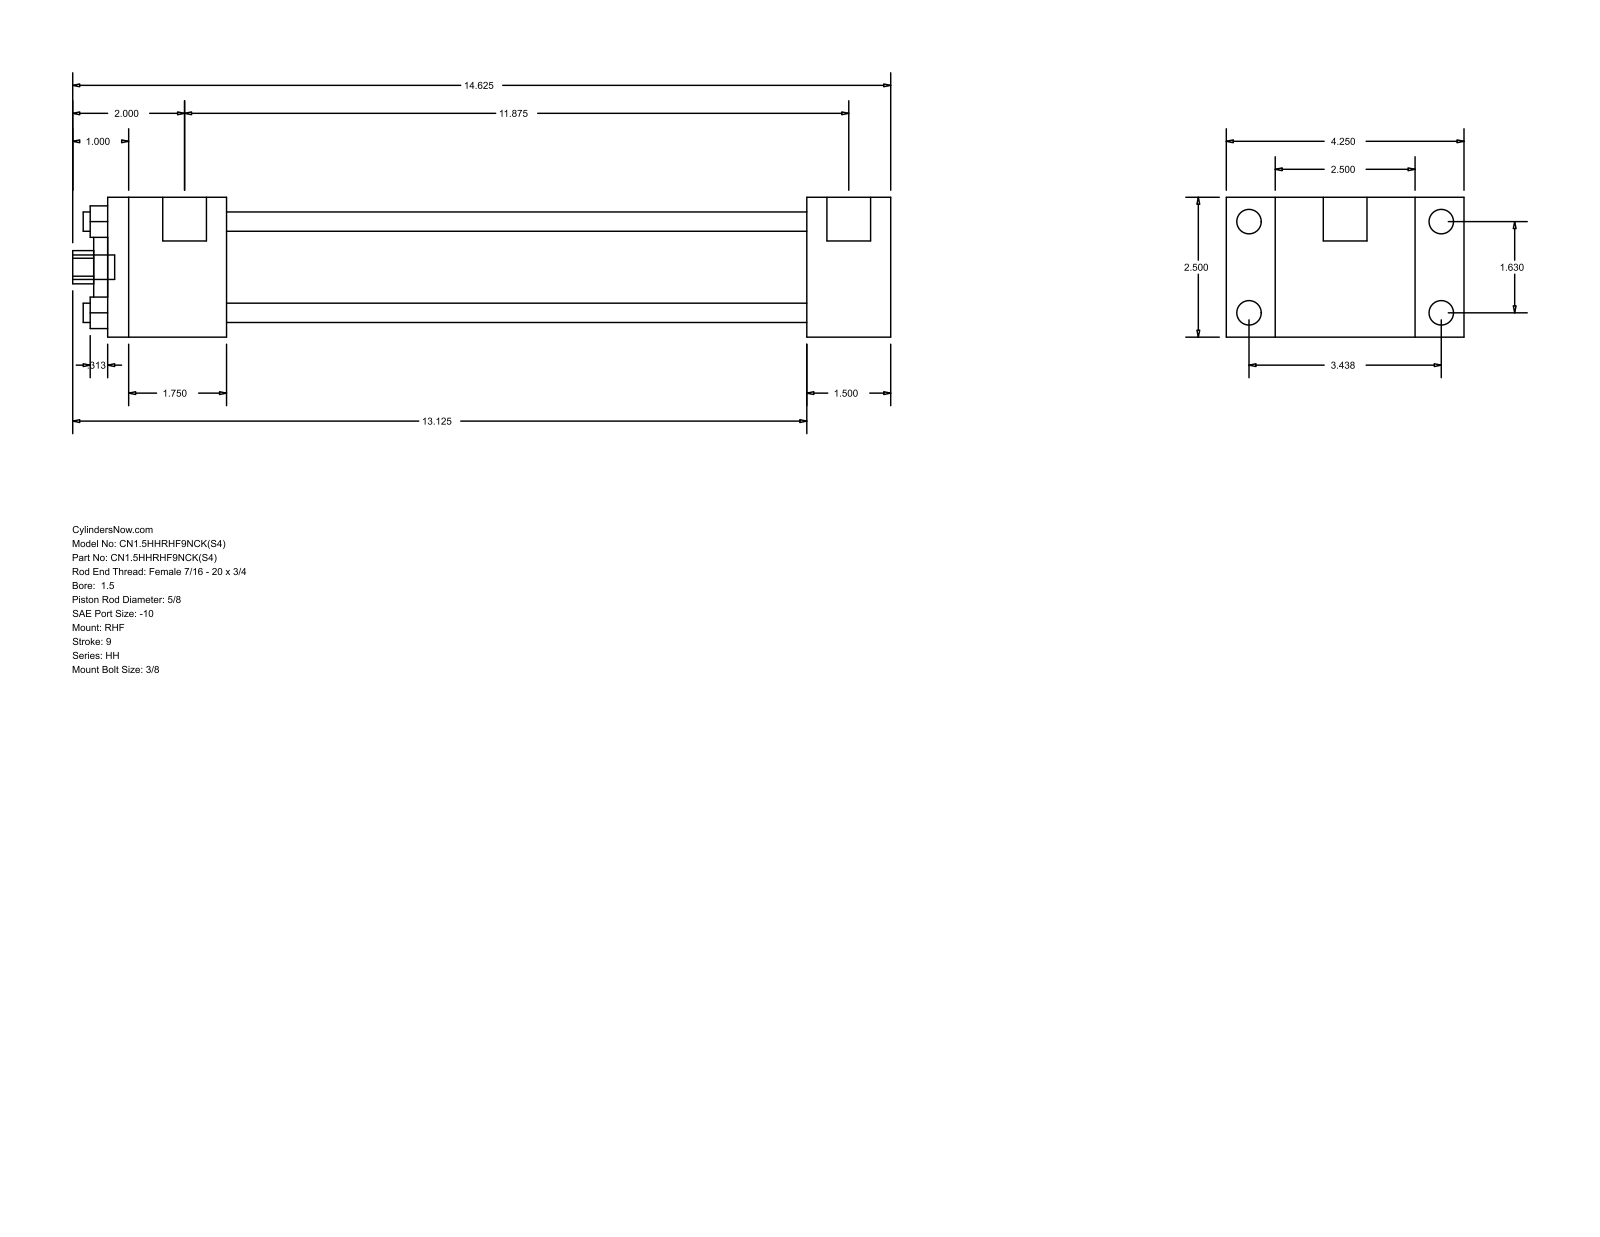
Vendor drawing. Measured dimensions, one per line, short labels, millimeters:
name: HH_RHF__0150_0.625
written by: GSSL Pune (CONFIG_CONTROL_DESIGN)
unit: mm
bodies: 0 solids, 88 faces (60 planar, 28 cylindrical, 0 other)
size: 371.48 × 107.95 × 63.5
holes: 4× ⌀8.76, 1× ⌀15.88, 1× ⌀28.57, 1× ⌀44.45
bosses: 4× ⌀11.13, 4× ⌀5.56, 2× ⌀19.84, 1× ⌀11.11
rounds: 1× R7.54
face distances: 63.5, 38.1, 22.23, 85.73, 317.5, 355.6, 107.96, 53.97, 263.53, 301.63
hole spacings: 29.27, 41.4, 58.55
